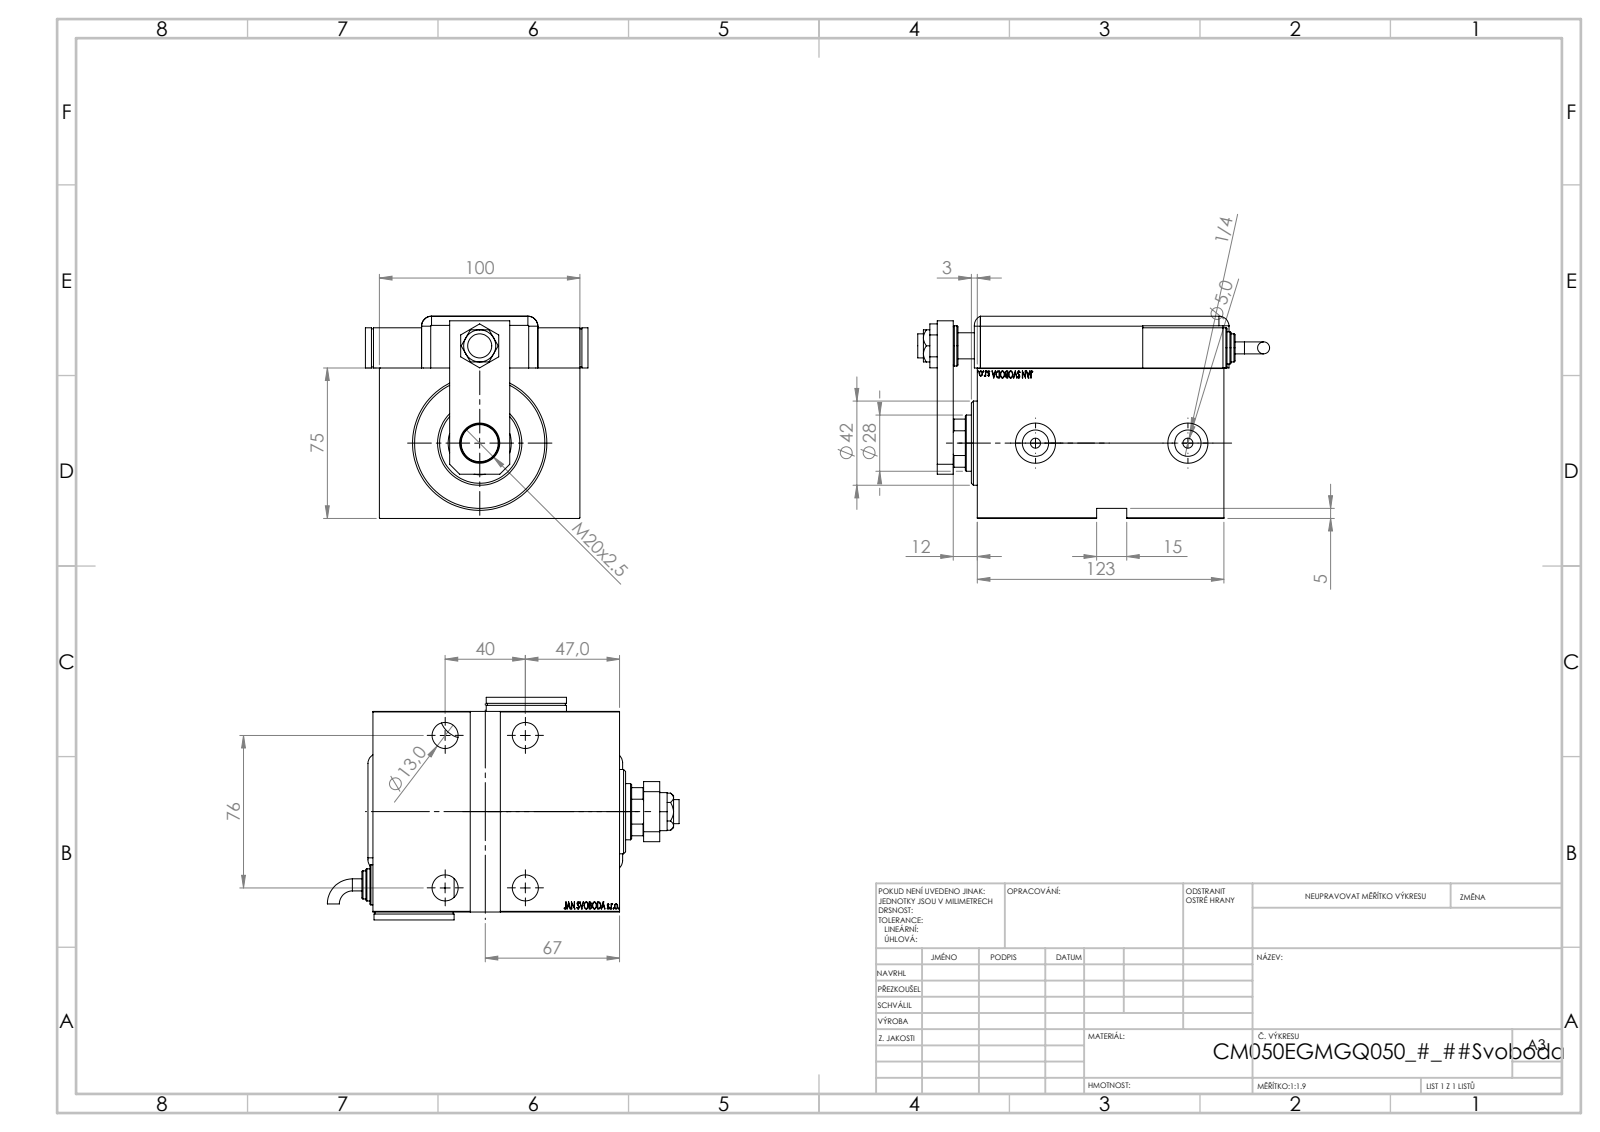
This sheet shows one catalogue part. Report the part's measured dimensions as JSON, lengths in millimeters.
{"part_name": "ZARAZKA_Q; V450CM_E_VCP; TYC; NUT_D19 (+7 more)", "step_written_by": "SolidWorks 2019 (CONFIG_CONTROL_DESIGN)", "units": "millimeters", "bodies": {"solids": 13, "faces": 1242, "planar": 618, "cylindrical": 107, "other": 517}, "overall_size": [175.46, 111, 100.8], "volume_mm3": 953389, "surface_area_mm2": 180462, "round_holes": [[13, 5], [19, 4], [20, 3], [4, 2], [5, 2], [8, 2], [13.16, 2], [12, 1], [14, 1], [18.5, 1], [28, 1], [31.5, 1]], "round_bosses_or_shafts": [[20, 3], [16, 2], [14, 2], [6, 2], [52, 1], [42, 1]], "partial_cylinders_radius": [[5, 9], [10, 1], [13.5, 1]], "face_to_face_distances": [3, 75, 100, 123, 100.8, 25.8, 14, 20, 109, 8], "hole_center_spacings": [76, 40, 47.2, 61.22, 82.87, 85.88, 91.59, 20]}
